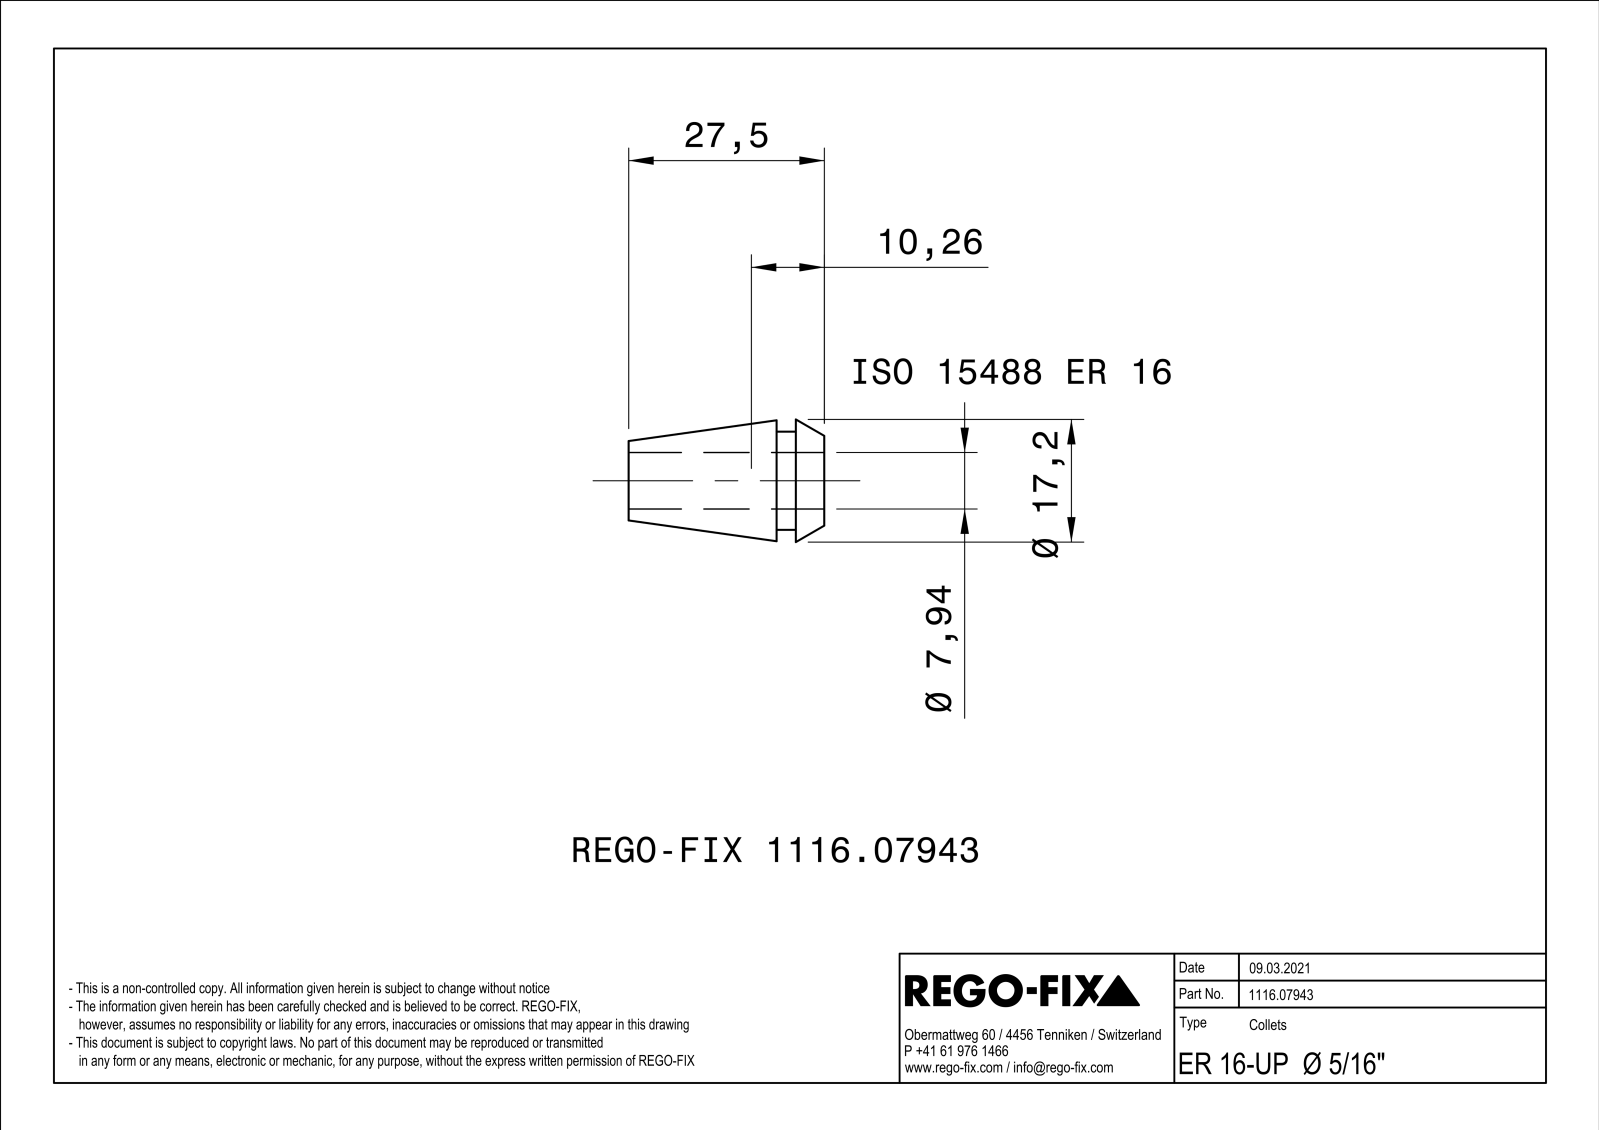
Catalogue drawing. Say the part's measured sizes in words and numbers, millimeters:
The part is named "NOCUT". Its 3-D file was written by "SIEMENS PLM Software Solid Edge ST10 (AUTOMOTIVE_DESIGN)". It is 1 solid with 153 faces: 72 planar, 25 cylindrical and 56 other. Overall it measures 27.5 by 17.24 by 17.24 millimeters. Its volume is 2 303 cubic millimeters and its surface area 4 164 square millimeters. Round holes: 1 of diameter 7.94. Round bosses or shafts: 1 of diameter 13.8. Partial cylindrical surfaces (rounded edges, fillets, slot ends): 8 of radius 0.3. The main face-to-face distances are 0.6, 4, 6.7, 2.7, 27.5, 23.5, 20.8.
